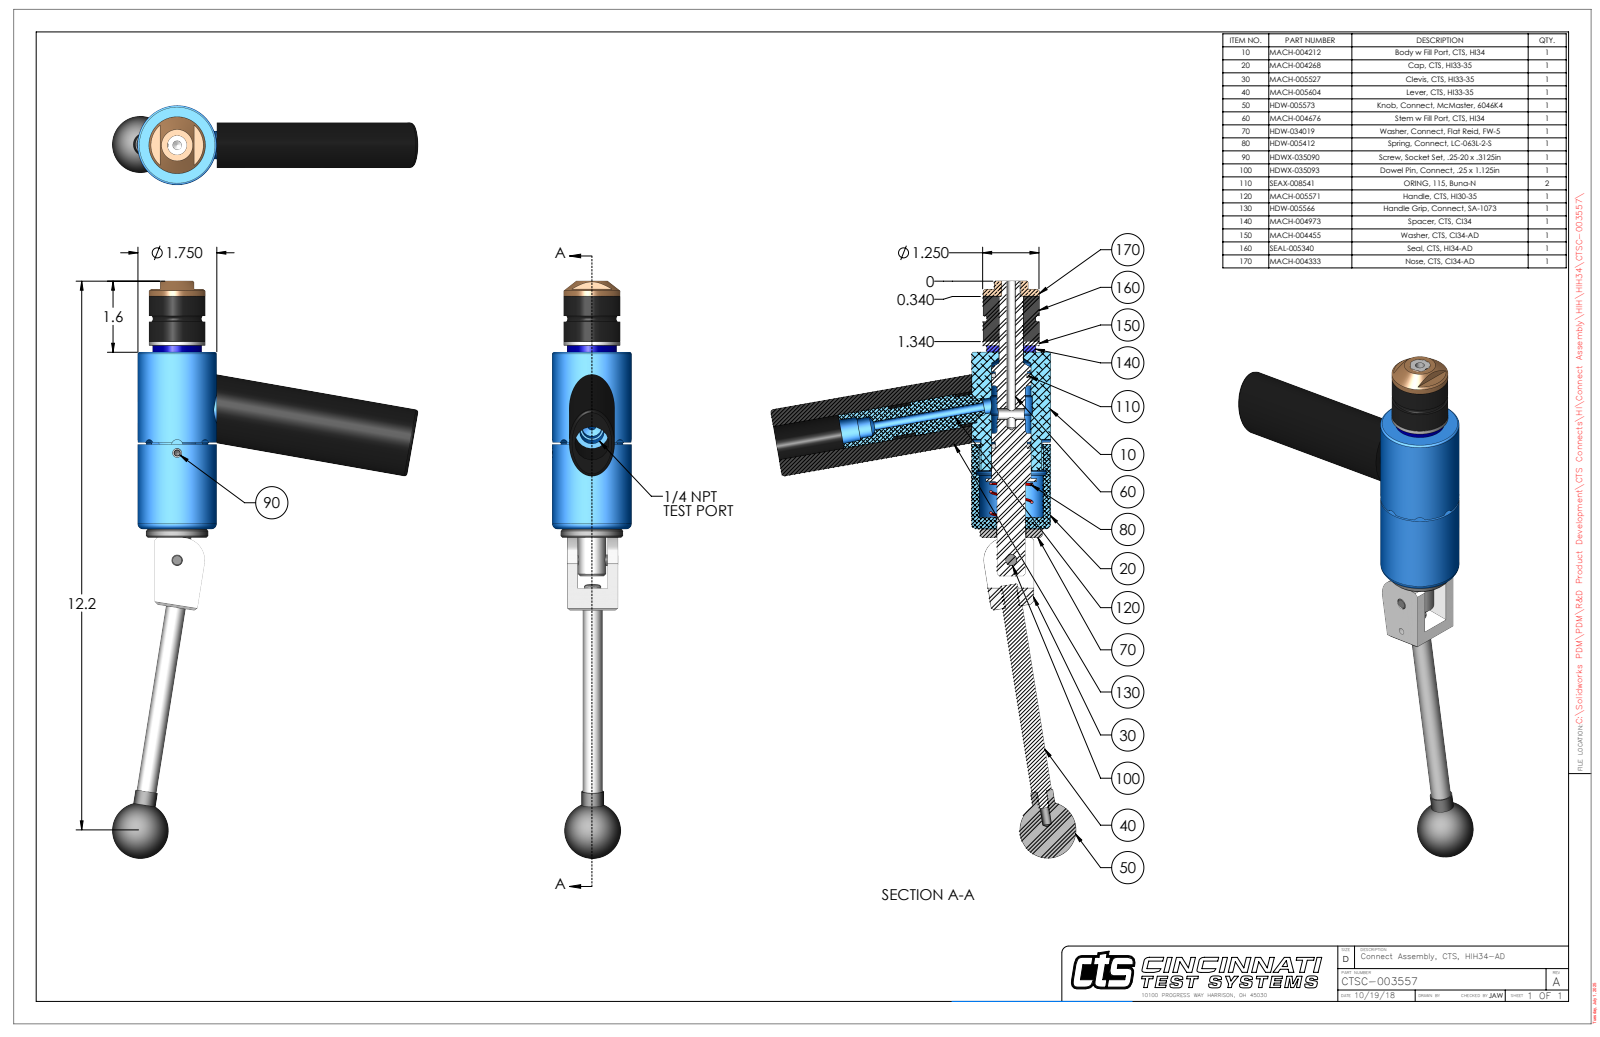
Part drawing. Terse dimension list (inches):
name: CTSC-003557
written by: SolidWorks 2023 (AUTOMOTIVE_DESIGN)
unit: in
bodies: 11 solids, 306 faces (109 planar, 126 cylindrical, 71 other)
size: 12.795 × 6.763 × 1.75
volume: 18.5 in³; area: 118.2 in²
holes: 2× ⌀0.201, 1× ⌀0.15, 1× ⌀0.187, 1× ⌀0.204, 1× ⌀0.249, 1× ⌀0.25, 1× ⌀0.251, 1× ⌀0.313, 1× ⌀0.422, 1× ⌀0.438, 1× ⌀0.53, 1× ⌀0.541
bosses: 2× ⌀0.5, 2× ⌀0.44, 2× ⌀0.25, 1× ⌀1.75, 1× ⌀1.38, 1× ⌀1.25, 1× ⌀1.09, 1× ⌀0.75
rounds: 5× R0.125, 2× R0.029, 1× R0.151, 1× R0.33, 1× R0.5, 1× R0.695, 1× R0.826
face distances: 3.921, 1.237, 5.158, 1, 0.237, 4.158, 1.094, 0.094, 0.143, 4.064
hole spacings: 0.74, 2.376, 3.116
